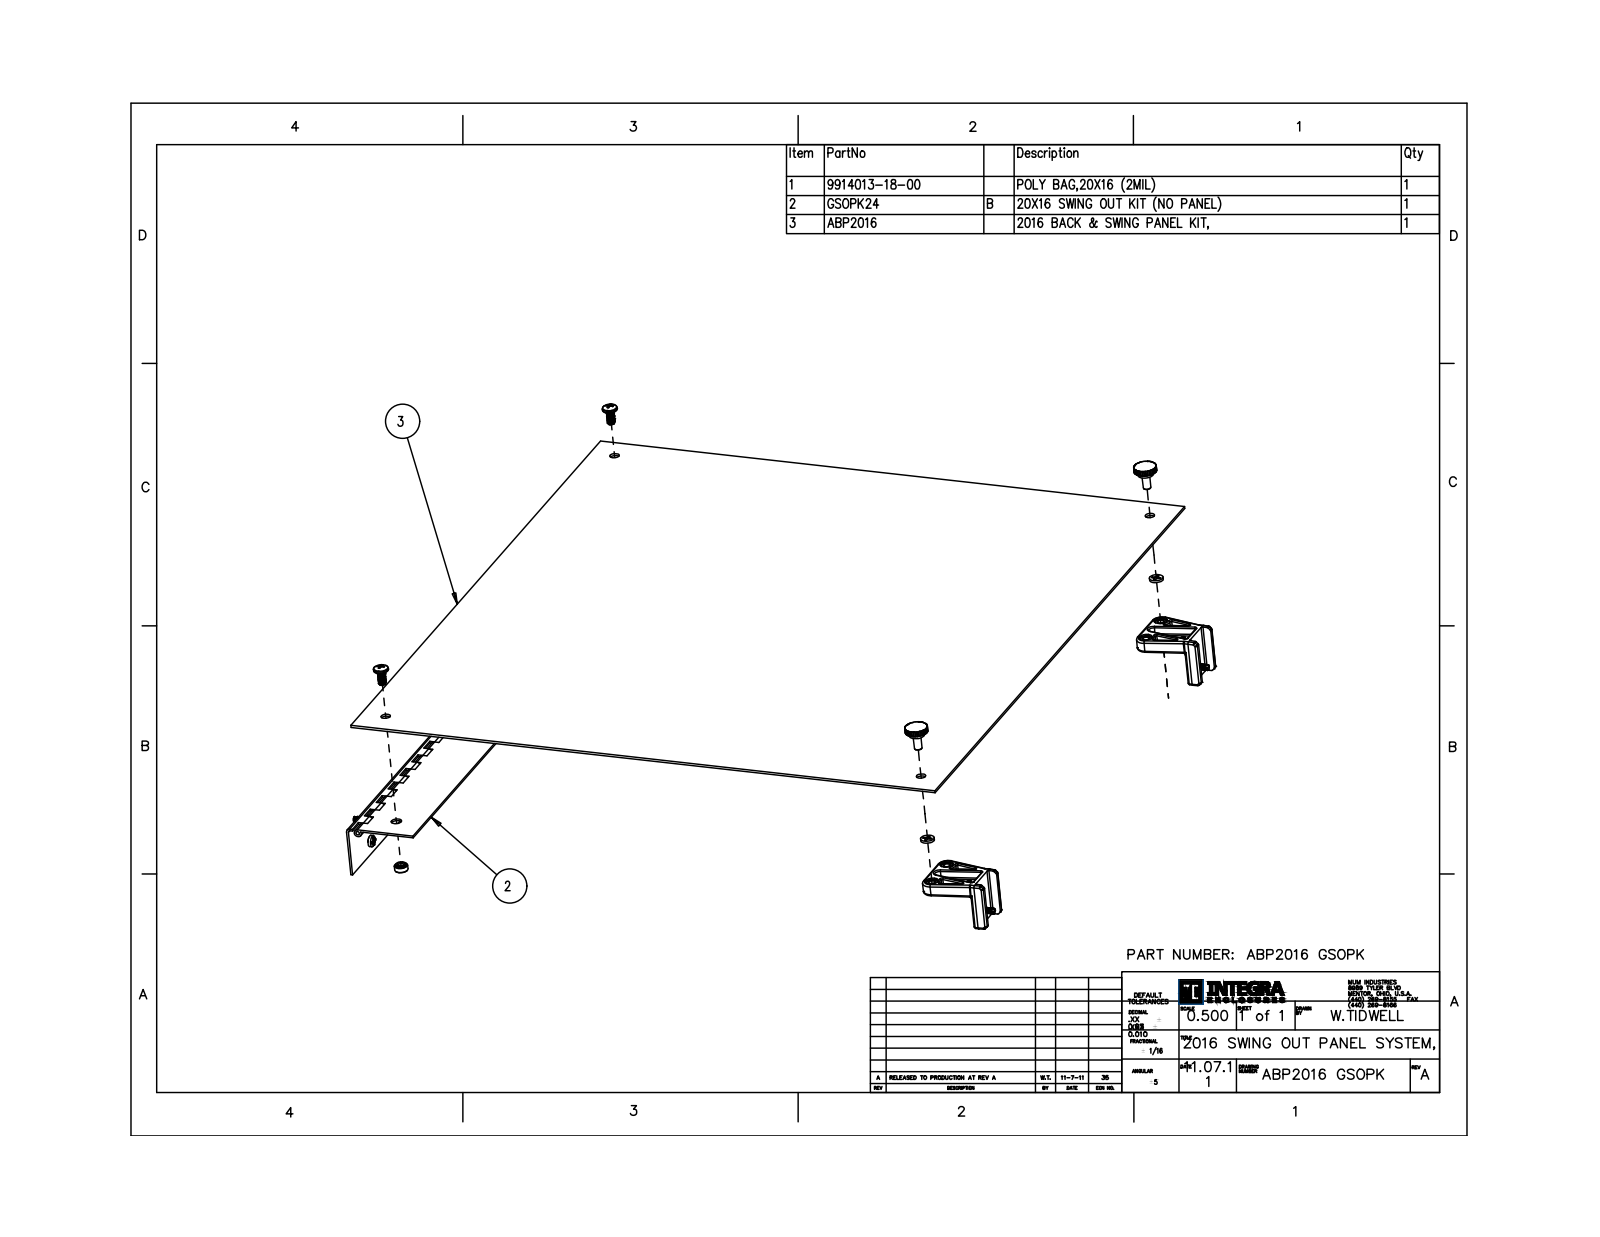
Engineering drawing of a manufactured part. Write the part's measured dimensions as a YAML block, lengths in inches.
part_name: "ABP-2016GSOPK-P10"
step_written_by: "SolidWorks 2018 (AUTOMOTIVE_DESIGN)"
units: inches
bodies: {solids: 25, faces: 2834, planar: 1794, cylindrical: 582, other: 458}
overall_size: [18.996, 18.09, 1.98]
volume: 30.7
surface_area: 787.5
round_holes:
  - {diameter: 0.25, count: 9}
  - {diameter: 0.212, count: 8}
  - {diameter: 0.203, count: 4}
  - {diameter: 0.443, count: 4}
  - {diameter: 0.206, count: 2}
  - {diameter: 0.269, count: 2}
  - {diameter: 0.31, count: 2}
  - {diameter: 0.312, count: 2}
  - {diameter: 0.125, count: 1}
round_bosses_or_shafts:
  - {diameter: 0.375, count: 10}
  - {diameter: 0.19, count: 6}
  - {diameter: 0.492, count: 4}
  - {diameter: 0.35, count: 4}
  - {diameter: 0.507, count: 2}
  - {diameter: 0.241, count: 2}
  - {diameter: 0.25, count: 1}
partial_cylinders:
  - {radius: 0.01, count: 180}
  - {radius: 0.06, count: 55}
  - {radius: 0.04, count: 34}
  - {radius: 0.05, count: 4}
  - {radius: 0.106, count: 4}
  - {radius: 0.125, count: 4}
  - {radius: 0.31, count: 4}
  - {radius: 0.373, count: 2}
face_to_face_distances: [0.08, 0.063, 0.143, 0.16, 17.312, 17.25, 17.152, 17.09, 17, 14.88]
hole_center_spacings: [0.02, 1.25, 17, 17.985, 18.25, 23.154, 0.013, 0.75]
